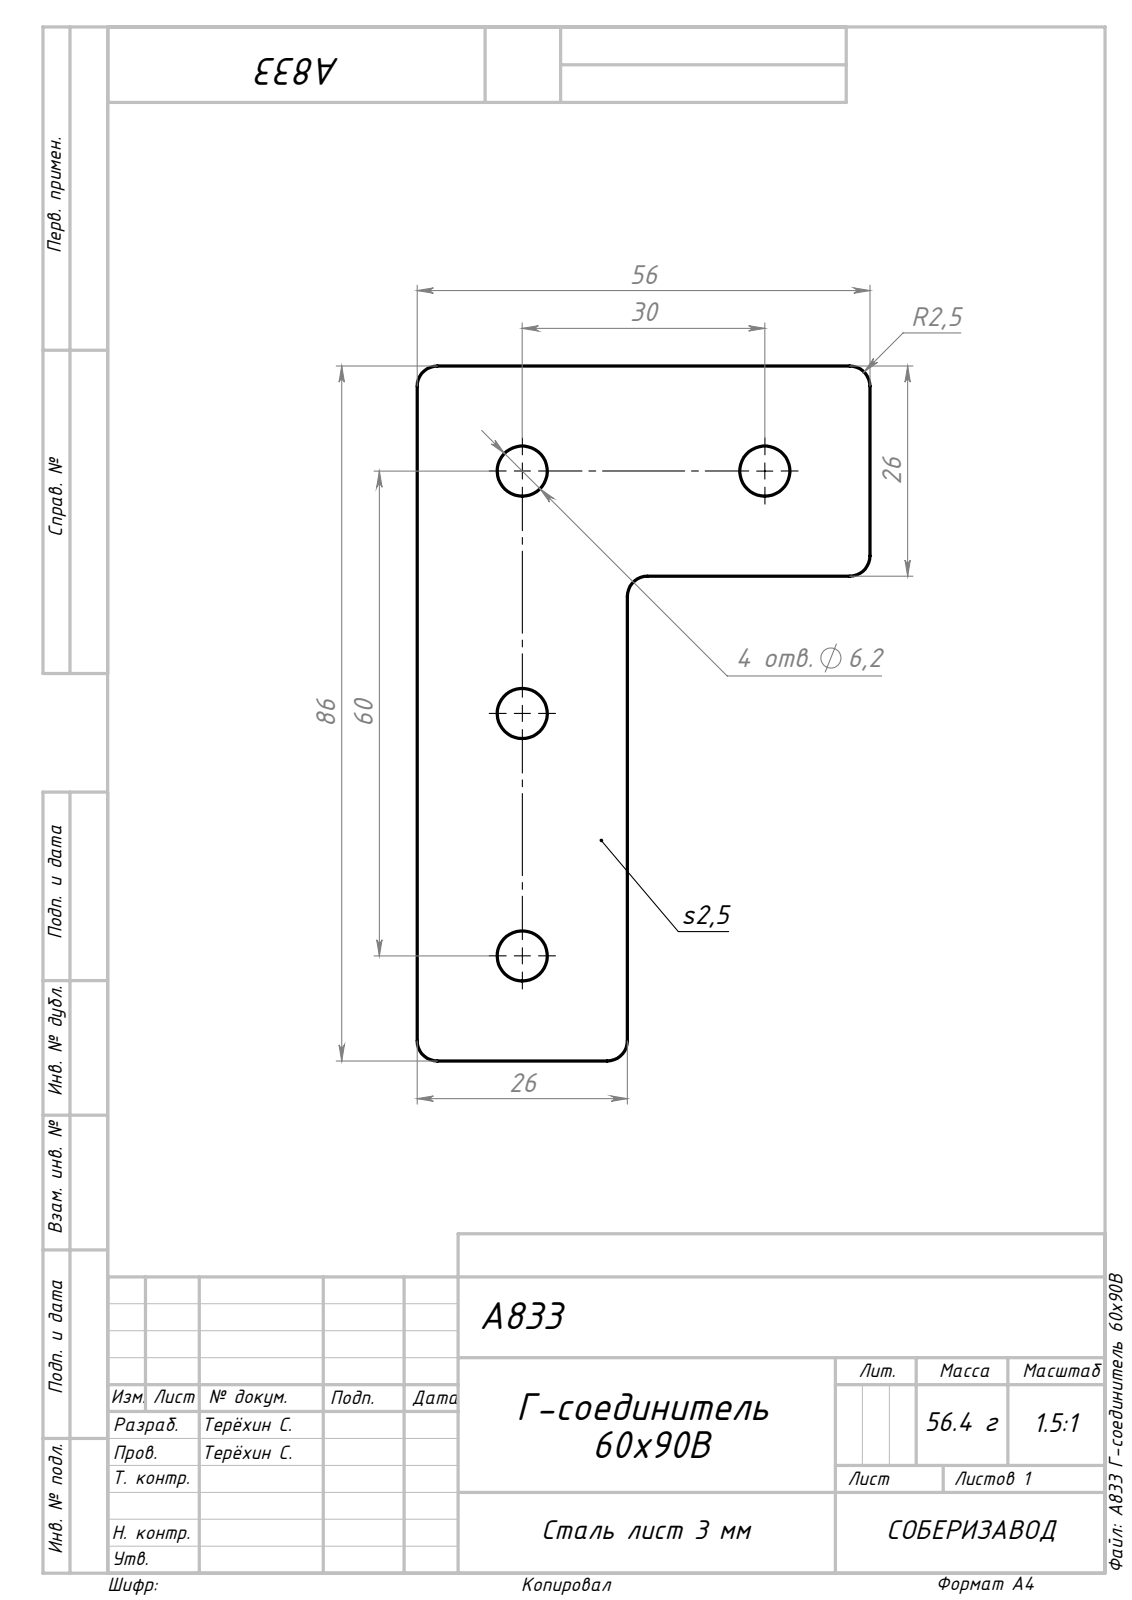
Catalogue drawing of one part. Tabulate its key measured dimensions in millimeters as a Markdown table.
| quantity | value |
| --- | --- |
| part name | A833 Г-соединитель 60х90В_00; Сборка8 |
| STEP written by | SolidWorks 2022 (AUTOMOTIVE_DESIGN) |
| units | millimeters |
| bodies | 1 solid, 22 faces (8 planar, 14 cylindrical, 0 other) |
| overall size | 86 × 56 × 2.5 |
| volume | 7 225 mm³ |
| surface area | 6 668 mm² |
| round holes (diameter × count) | 6.2 × 4 |
| partial cylindrical surfaces (radius × count) | 2.5 × 6 |
| main face-to-face distances | 2.5, 26, 86, 60, 56, 30 |
| hole center spacings | 30, 42.43, 60, 67.08 |
